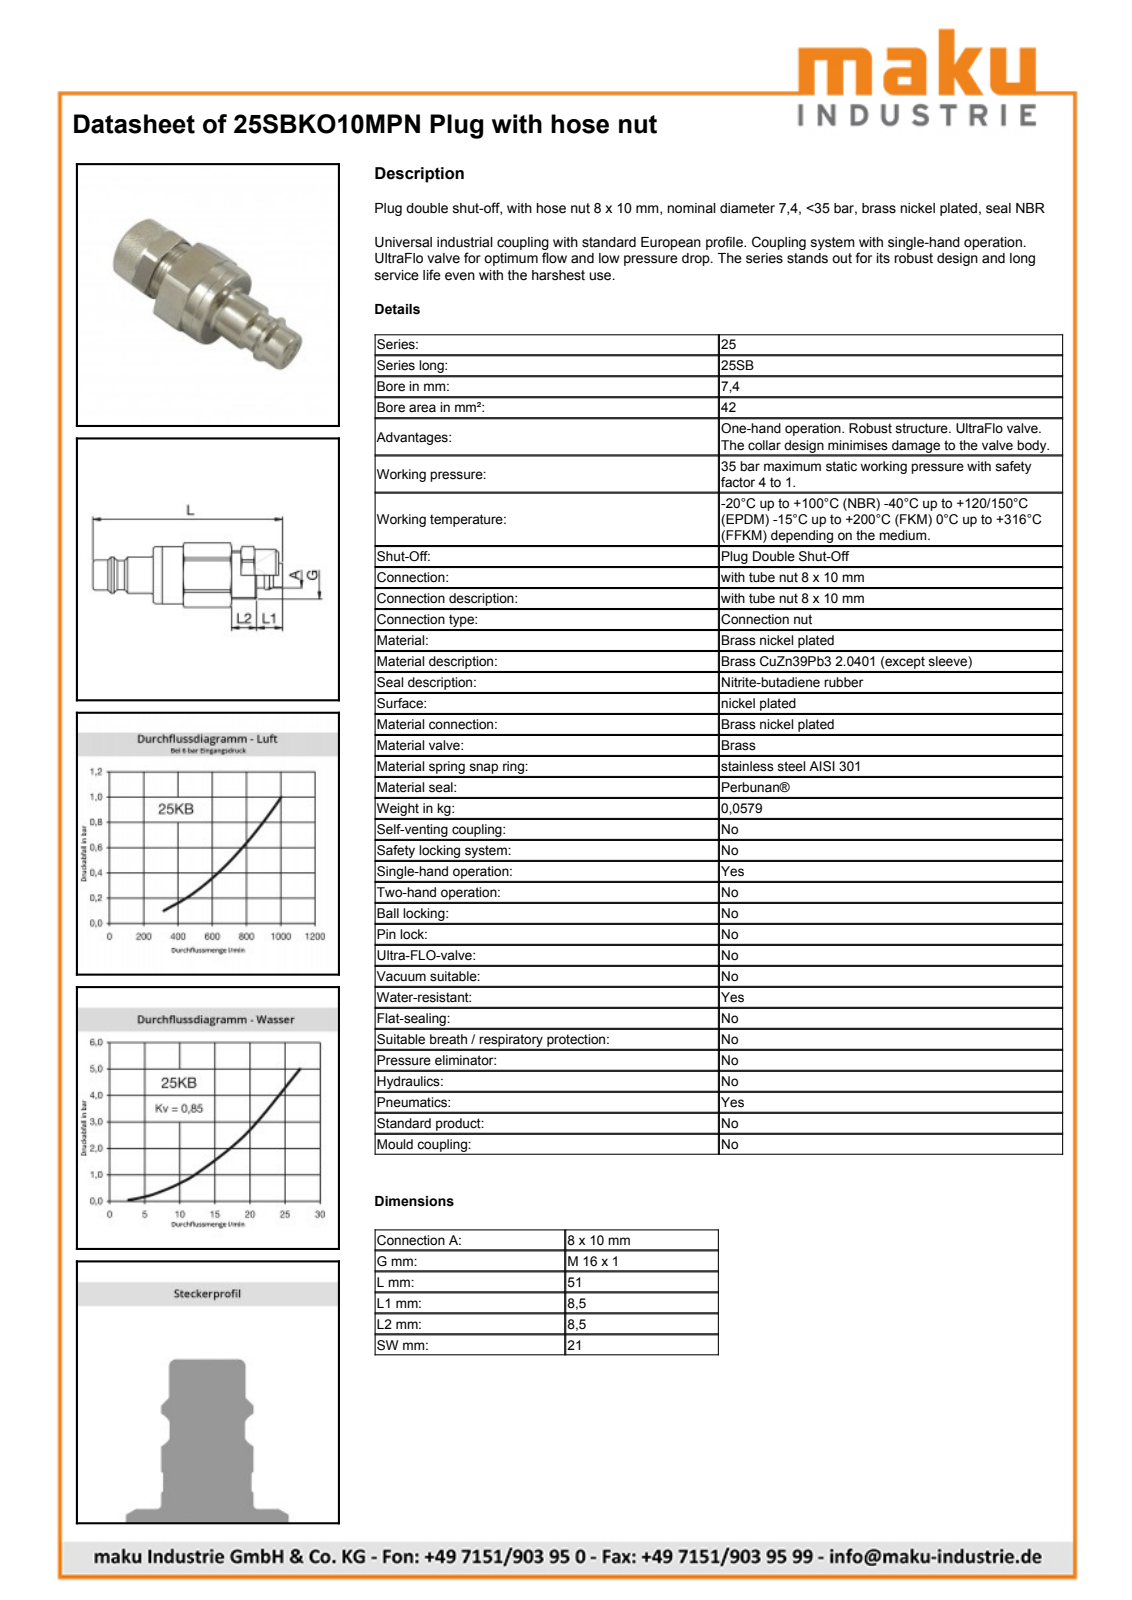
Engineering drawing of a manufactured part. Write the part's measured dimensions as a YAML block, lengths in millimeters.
part_name: "D109869"
step_written_by: "Autodesk Inventor 2013 (AUTOMOTIVE_DESIGN)"
units: millimeters
bodies: {solids: 1, faces: 99, planar: 26, cylindrical: 29, other: 44}
overall_size: [51.1, 23.37, 22.82]
volume: 9770
surface_area: 4638
round_holes:
  - {diameter: 10.2, count: 1}
  - {diameter: 15.46, count: 1}
  - {diameter: 17, count: 1}
round_bosses_or_shafts:
  - {diameter: 21, count: 1}
  - {diameter: 16.5, count: 1}
  - {diameter: 16, count: 1}
  - {diameter: 14.97, count: 1}
  - {diameter: 14.6, count: 1}
  - {diameter: 12, count: 1}
  - {diameter: 10, count: 1}
  - {diameter: 9.75, count: 1}
partial_cylinders:
  - {radius: 9.57, count: 1}
  - {radius: 11.85, count: 1}
face_to_face_distances: [21, 17, 4.5, 14.1, 22.5, 6.5, 27, 12.9, 8.4, 29]
